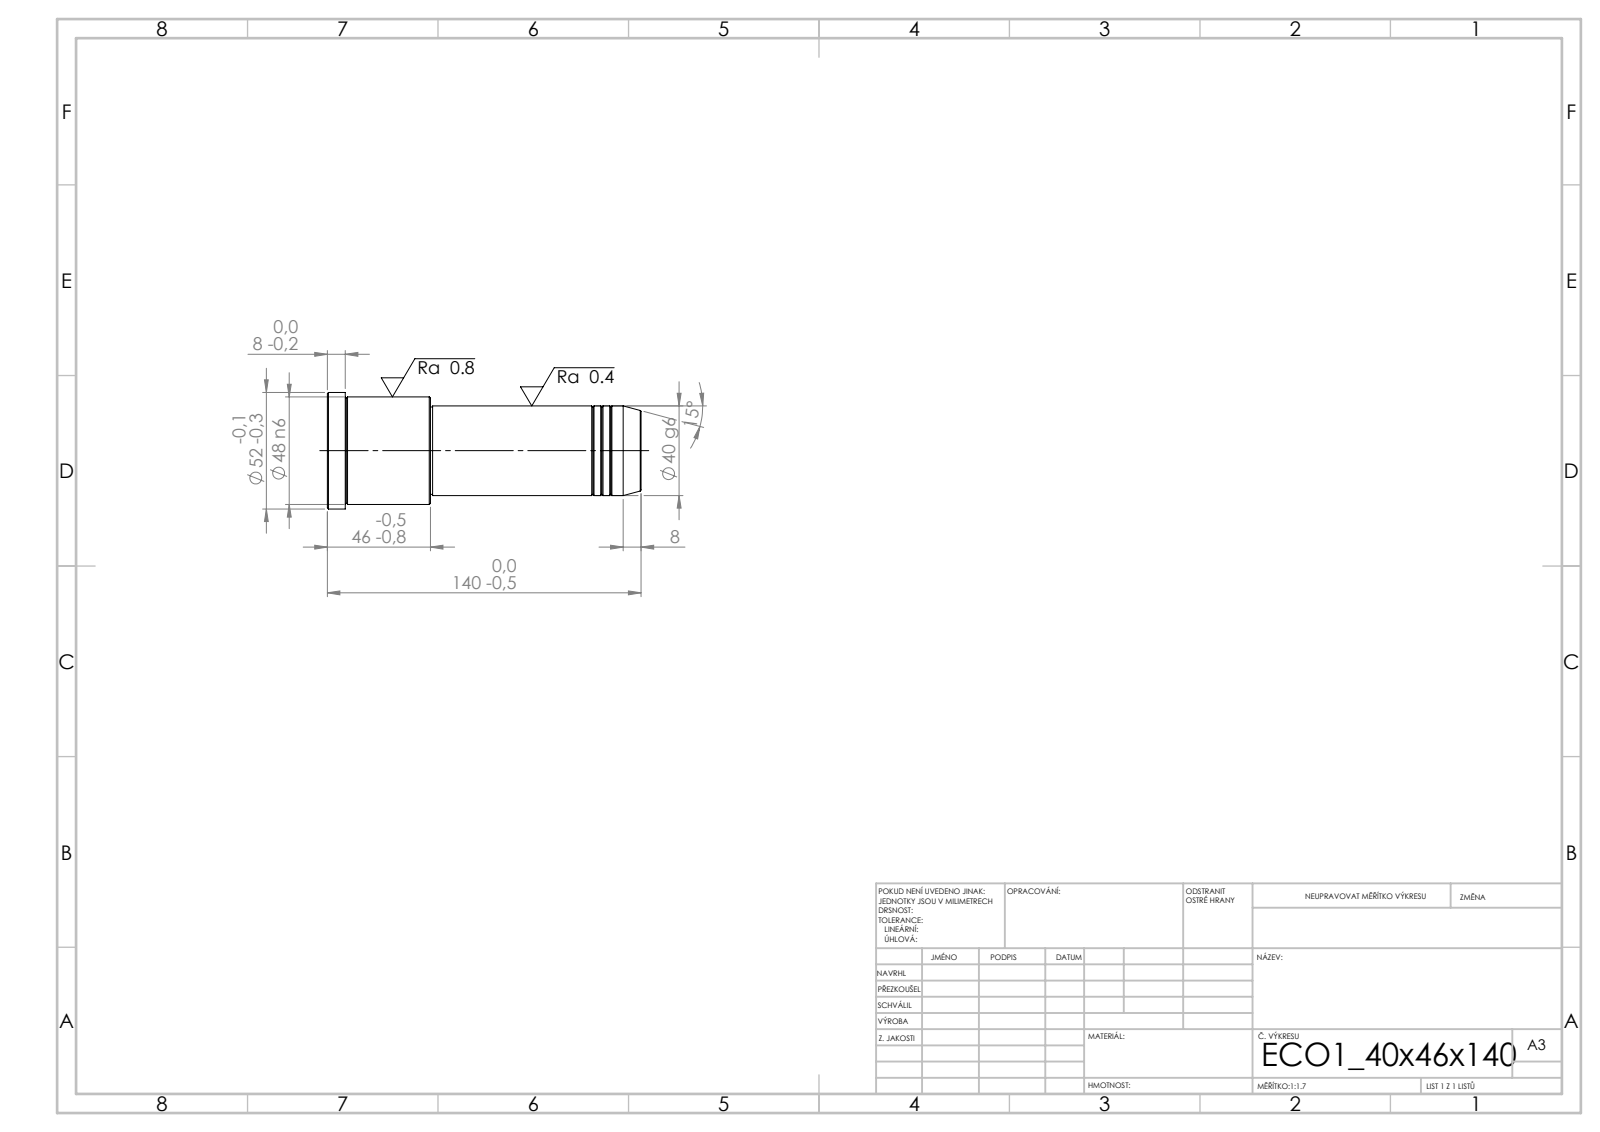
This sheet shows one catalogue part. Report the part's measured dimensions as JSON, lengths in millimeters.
{"step_written_by": "SolidWorks 2019 (CONFIG_CONTROL_DESIGN)", "units": "millimeters", "bodies": {"solids": 1, "faces": 43, "planar": 5, "cylindrical": 14, "other": 24}, "overall_size": [140, 52, 52], "volume_mm3": 202528, "surface_area_mm2": 23126, "round_bosses_or_shafts": [[52, 1], [48, 1], [40, 1], [39, 1]], "face_to_face_distances": [140, 94, 46, 132, 38, 8, 93, 1, 39, 47]}
